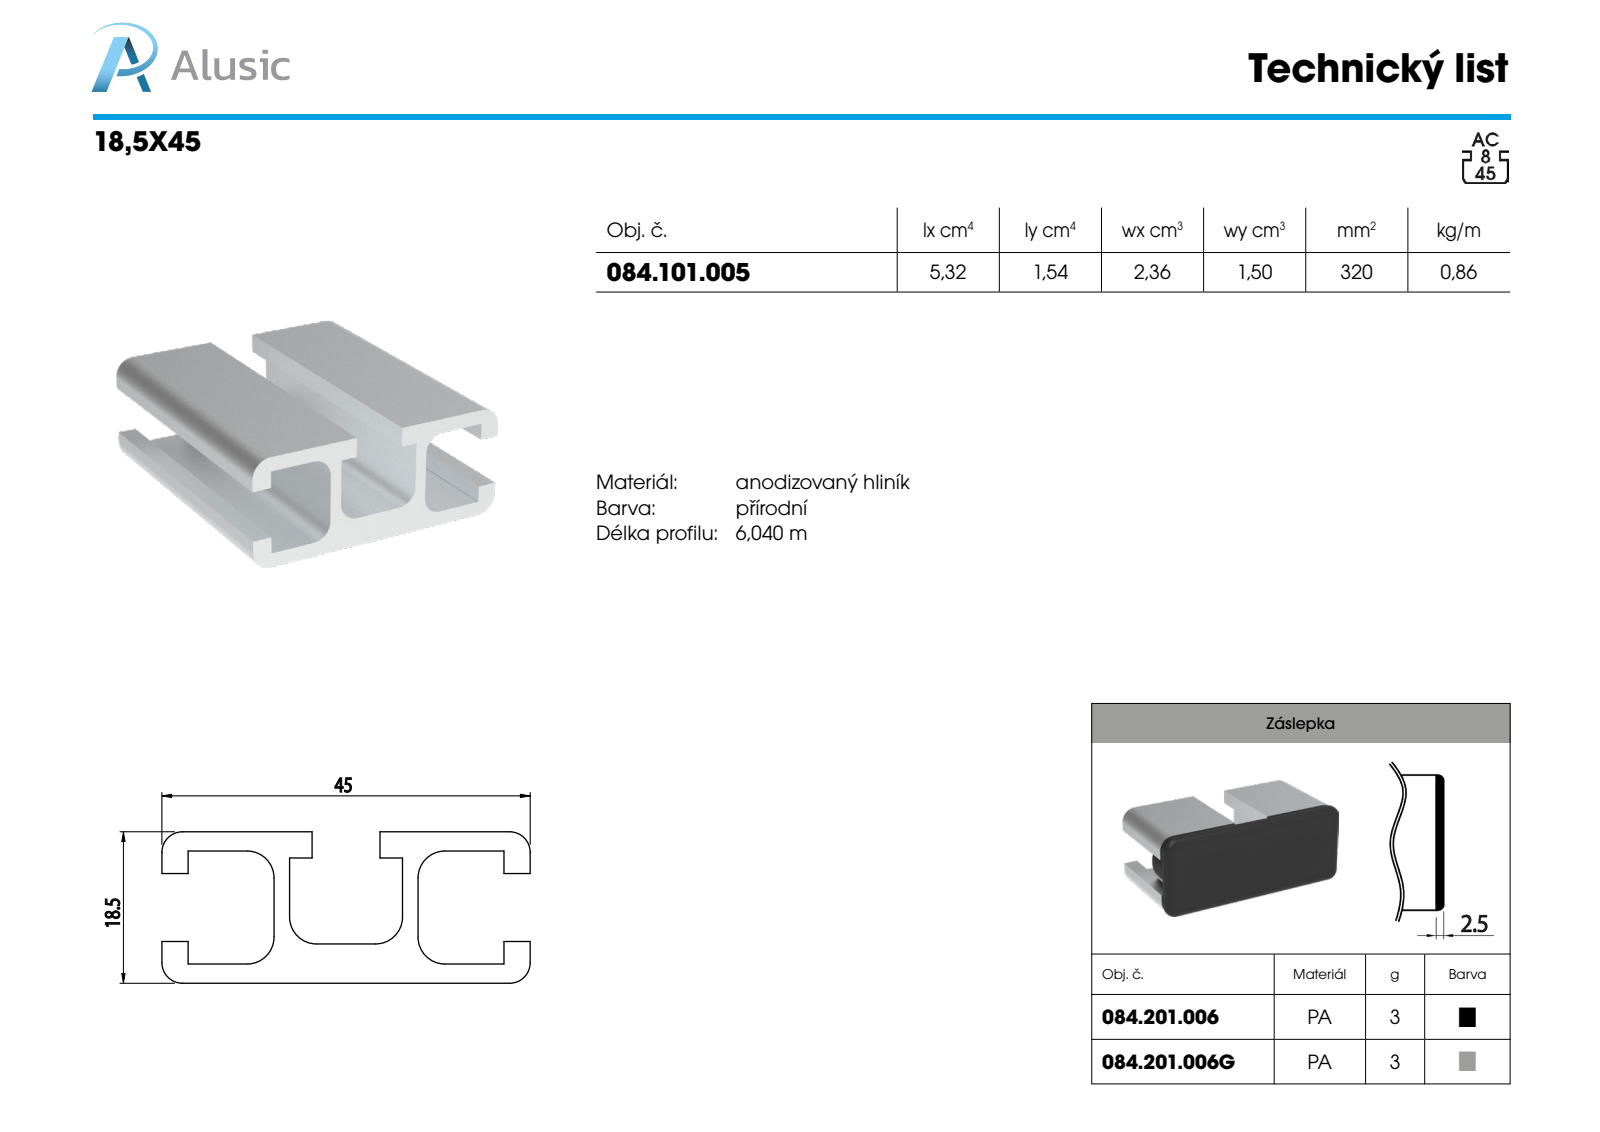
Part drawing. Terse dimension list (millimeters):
name: 084.201.006
written by: SolidWorks 2011 (CONFIG_CONTROL_DESIGN)
unit: mm
bodies: 1 solid, 34 faces (10 planar, 16 cylindrical, 8 other)
size: 45 × 18.5 × 12.5
volume: 2 805 mm³; area: 3 188 mm²
holes: 2× ⌀9.5
bosses: 2× ⌀12
rounds: 4× R2, 4× R2.5
face distances: 2.5, 12.5, 10, 18.5, 45
hole spacings: 29
